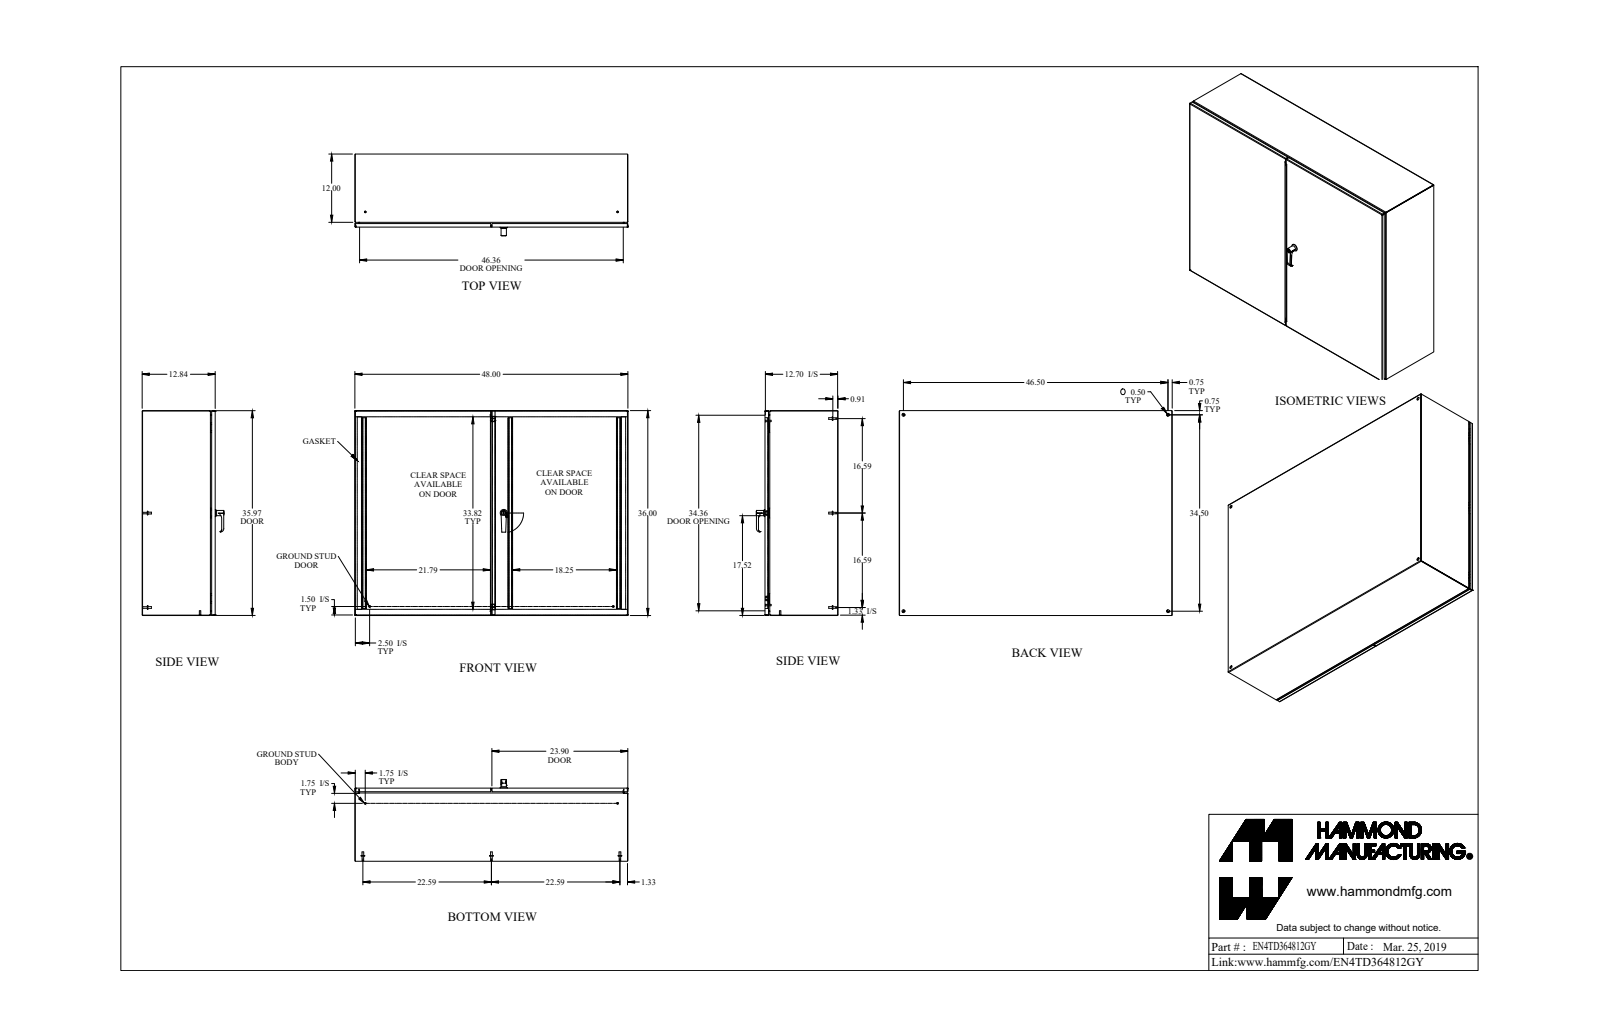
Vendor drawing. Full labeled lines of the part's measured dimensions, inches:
Part name (STEP PRODUCT): EN4TD364812GY
STEP written by: SolidWorks 2018 (AUTOMOTIVE_DESIGN)
Units: inches
Bodies: 89 solids, 2211 faces (986 planar, 806 cylindrical, 419 other)
Overall size (bounding box): 48 × 36 × 14.372
Volume: 480.7 in³ · Surface area: 12 718 in²
Round holes (diameter × count): ⌀0.196 ×6, ⌀0.176 ×4, ⌀0.5 ×4, ⌀0.24 ×3, ⌀0.242 ×3, ⌀0.25 ×3, ⌀0.265 ×3, ⌀0.172 ×2, ⌀0.256 ×2, ⌀0.26 ×2, ⌀0.265 ×2, ⌀0.313 ×2
Round bosses / shafts (diameter × count): ⌀0.25 ×11, ⌀0.313 ×10, ⌀0.27 ×8, ⌀0.625 ×6, ⌀0.51 ×4, ⌀0.375 ×4, ⌀0.281 ×4, ⌀0.156 ×4
Partial cylindrical surfaces — rounded edges, fillets, slot ends (radius × count): R0.036 ×26, R0.108 ×26, R0.063 ×25, R0.094 ×20, R0.043 ×18, R0.081 ×18, R0.02 ×16, R0.016 ×15
Main face-to-face distances: 0.072, 12.77, 12.698, 12.842, 35.928, 47.928, 35.856, 36, 47.856, 48
Hole centre spacings: 0.787, 20.798, 25.752, 27.241, 30.718, 34.5, 46.5, 47.45
